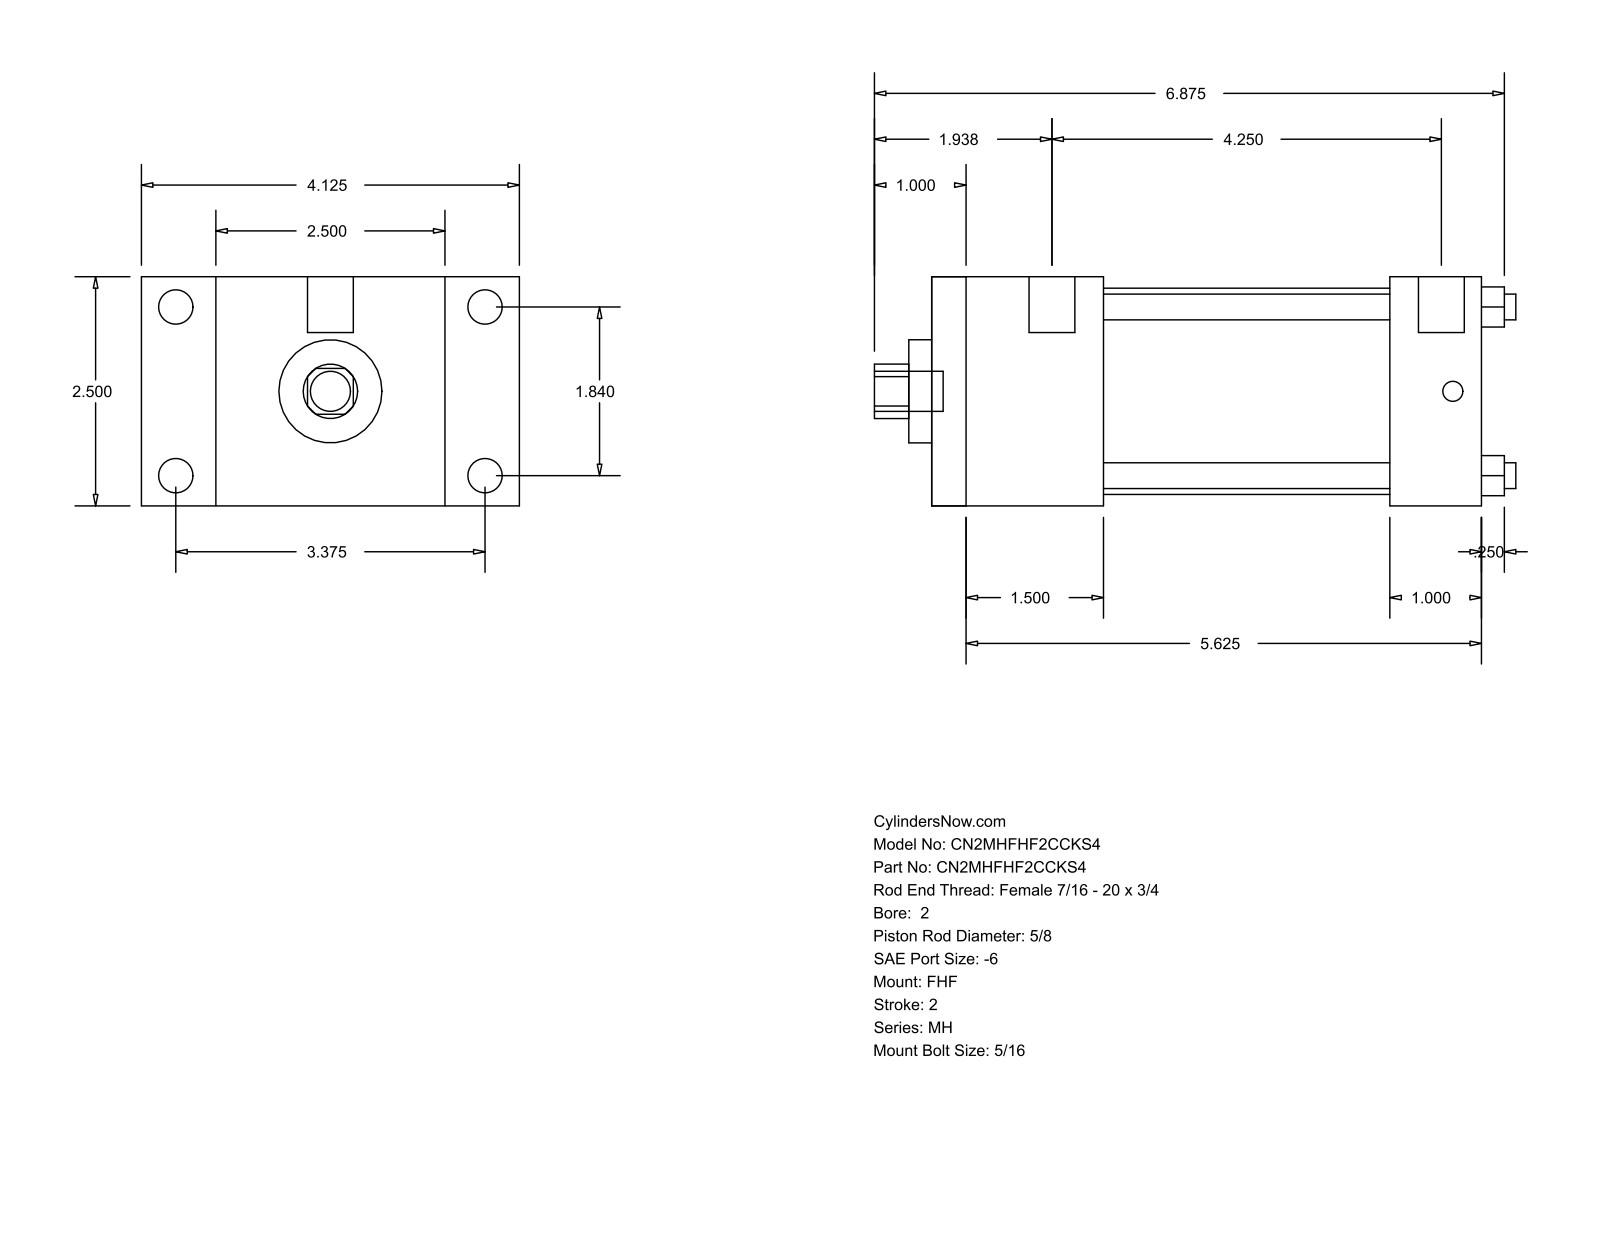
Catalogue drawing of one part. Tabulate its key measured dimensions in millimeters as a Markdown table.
| quantity | value |
| --- | --- |
| part name | MH_FHF__0200_0.625 |
| STEP written by | GSSL Pune (CONFIG_CONTROL_DESIGN) |
| units | millimeters |
| bodies | 0 solids, 88 faces (60 planar, 28 cylindrical, 0 other) |
| overall size | 177.8 × 104.78 × 63.5 |
| round holes (diameter × count) | 7.14 × 4, 15.88 × 1, 28.57 × 1, 57.15 × 1 |
| round bosses / shafts (diameter × count) | 9.53 × 4, 5.56 × 4, 12.7 × 2, 11.11 × 1 |
| partial cylindrical surfaces (radius × count) | 7.54 × 1 |
| main face-to-face distances | 63.5, 104.78, 47.62, 152.4, 20.64, 84.14, 25.4, 127, 79.38, 158.75 |
| hole center spacings | 33.05, 46.74, 66.1 |
